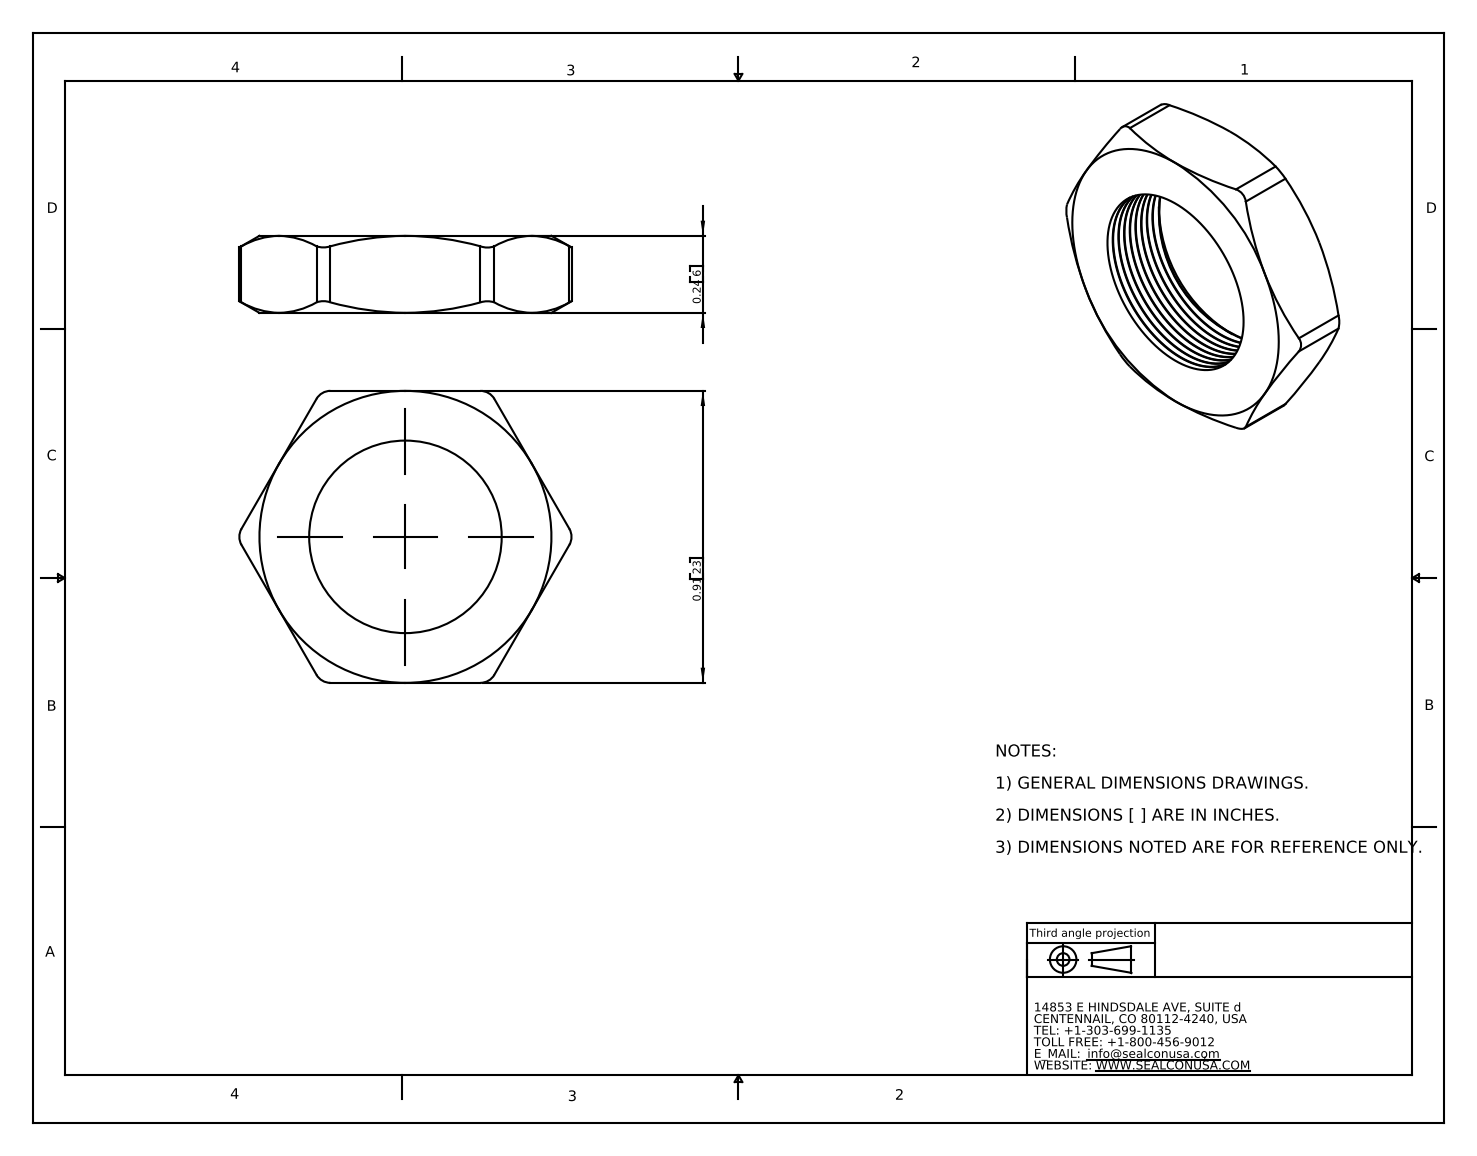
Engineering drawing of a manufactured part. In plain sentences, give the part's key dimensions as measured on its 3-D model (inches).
The part is named "NP-09-GY". Its 3-D file was written by "SolidWorks 2007 (CONFIG_CONTROL_DESIGN)". It is 1 solid with 87 faces: 8 planar, 25 cylindrical and 54 other. Overall it measures 1.035 by 0.91 by 0.24 inches. Its volume is 0.098 cubic inches and its surface area 2.426 square inches. Round holes: 1 of diameter 0.6. Partial cylindrical surfaces (rounded edges, fillets, slot ends): 6 of radius 0.05. The main face-to-face distances are 0.24, 0.91.
